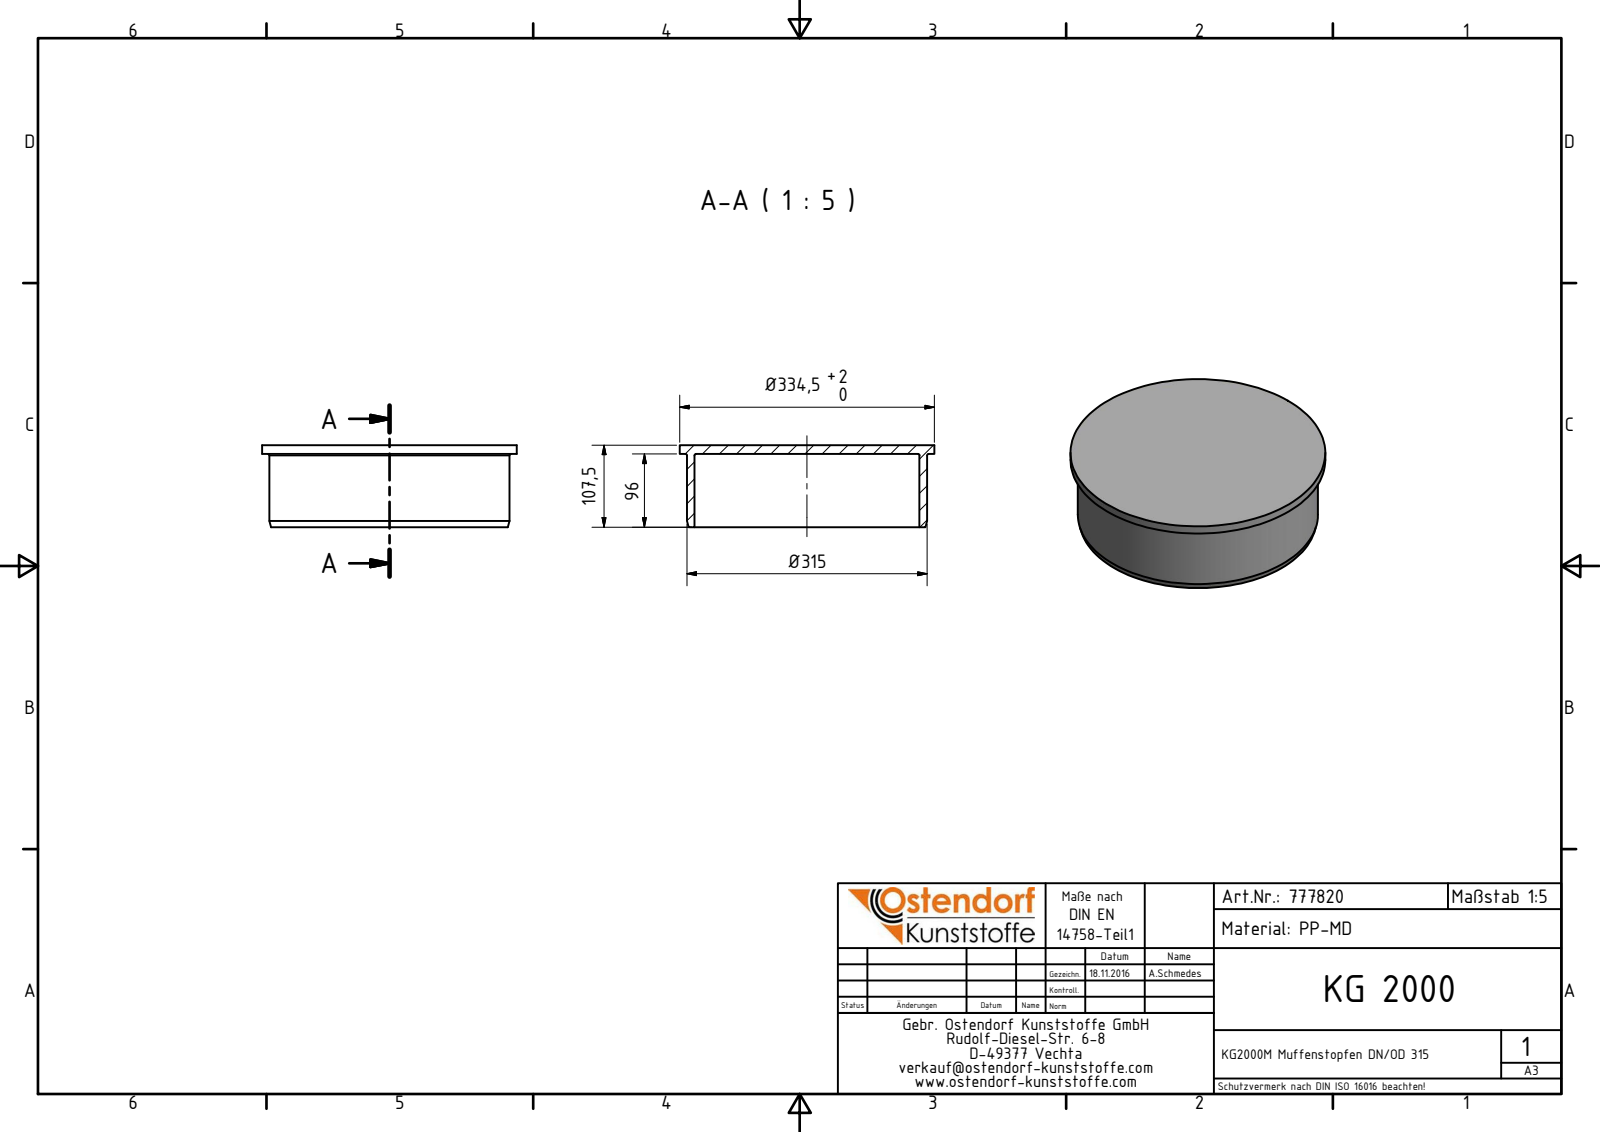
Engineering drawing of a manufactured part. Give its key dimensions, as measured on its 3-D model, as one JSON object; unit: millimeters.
{"part_name": "777820 KG2000M Muffenstopfen DN_OD 315", "step_written_by": "Autodesk Inventor 2016 (AUTOMOTIVE_DESIGN)", "units": "millimeters", "bodies": {"solids": 1, "faces": 10, "planar": 4, "cylindrical": 3, "other": 3}, "overall_size": [334.5, 334.5, 107.5], "volume_mm3": 1925000, "surface_area_mm2": 368463, "round_holes": [[295.3, 1]], "round_bosses_or_shafts": [[334.5, 1], [315.3, 1]], "face_to_face_distances": [11.5, 96, 107.5]}
